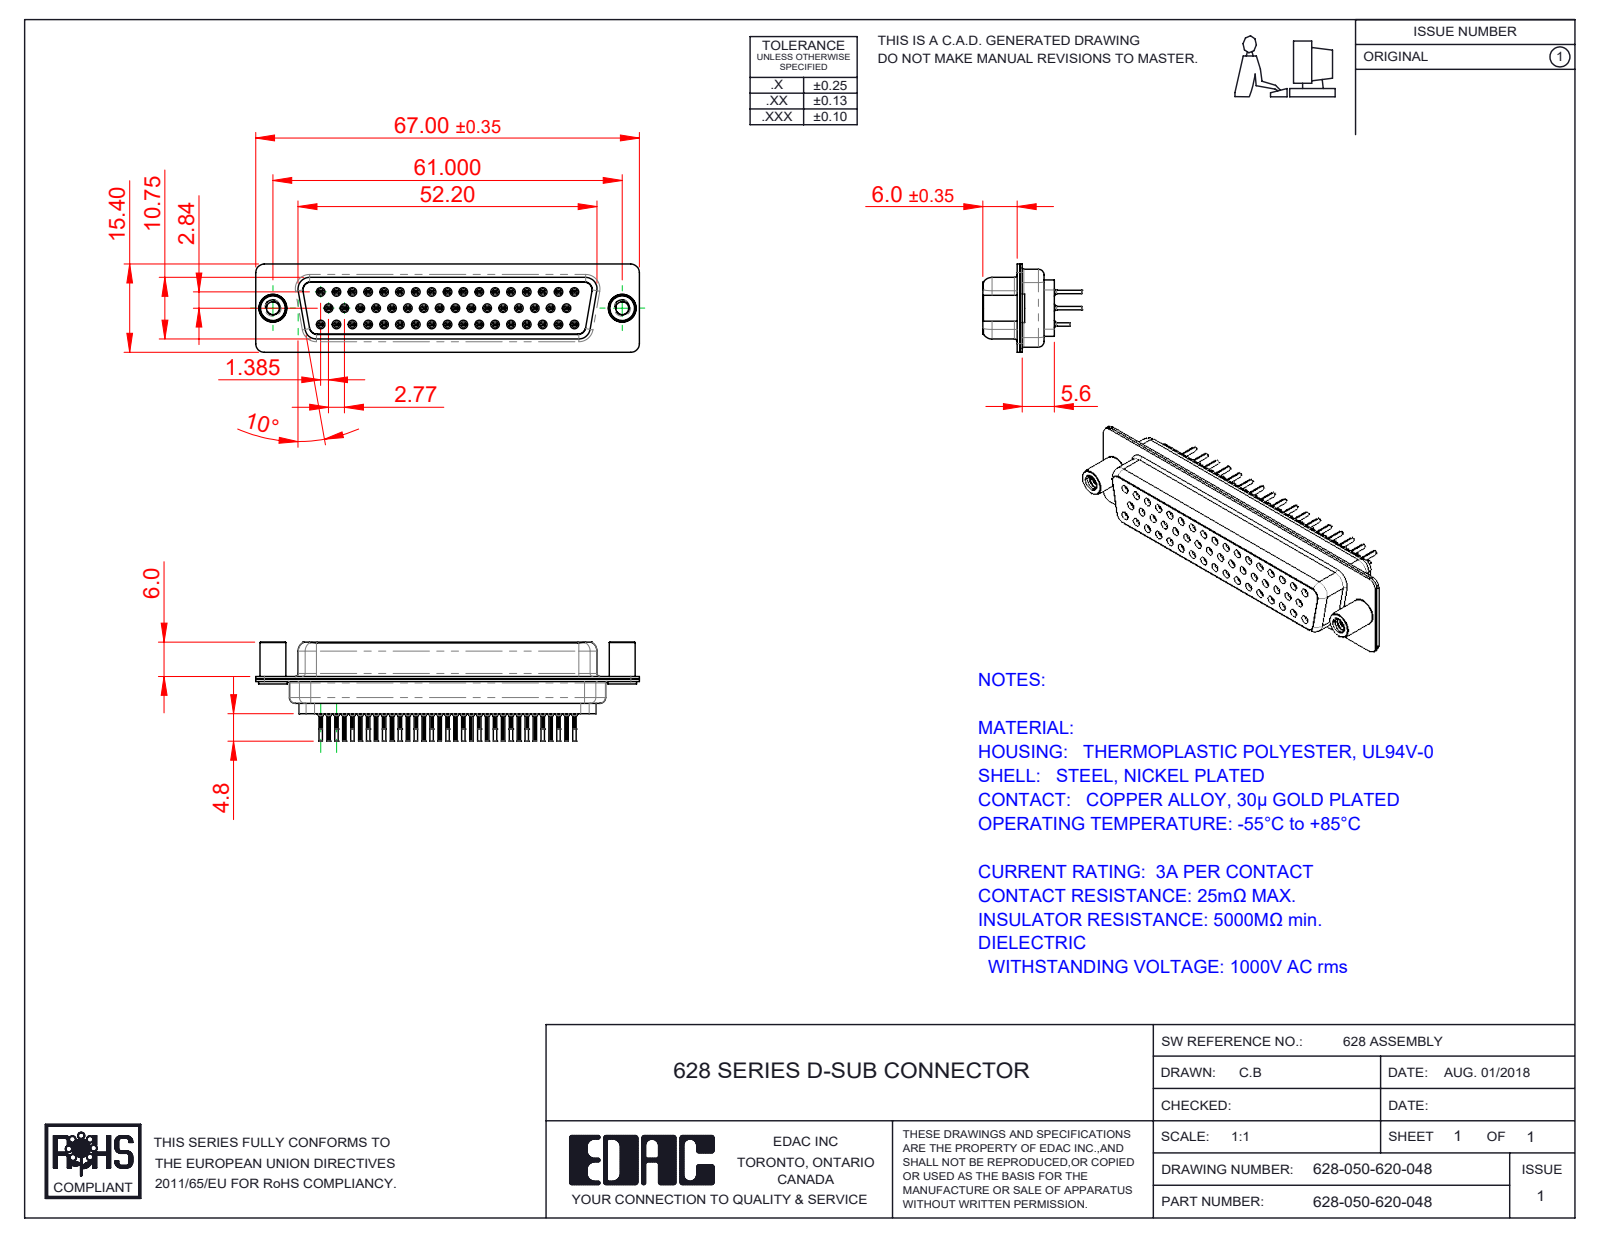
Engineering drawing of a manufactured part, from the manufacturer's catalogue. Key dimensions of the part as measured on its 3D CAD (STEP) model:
Part name (STEP PRODUCT): 628 Contact Row 1_20L; 628 Contact Row 2_20L; 628-050-620-048; 628 Shell Rear_50 Contacts (+4 more)
STEP written by: SolidWorks 2020 (CONFIG_CONTROL_DESIGN)
Units: millimetres
Bodies: 55 solids, 6663 faces (1619 planar, 1815 cylindrical, 3229 other)
Overall size (bounding box): 67 × 17.3 × 15.4
Volume: 6 786 mm³ · Surface area: 15 476 mm²
Round holes (diameter × count): ⌀0.2 ×50, ⌀0.8 ×50, ⌀0.9 ×50, ⌀1.1 ×50, ⌀1.6 ×50, ⌀1.7 ×17, ⌀2.26 ×2, ⌀4 ×2, ⌀4.05 ×2, ⌀4.85 ×2
Round bosses / shafts (diameter × count): ⌀2 ×50, ⌀1.5 ×50, ⌀1.2 ×50, ⌀0.6 ×50, ⌀5 ×2, ⌀4.95 ×2, ⌀4.8 ×2, ⌀4.5 ×2
Partial cylindrical surfaces — rounded edges, fillets, slot ends (radius × count): R0.1 ×100, R0.28 ×33, R1.5 ×16, R2 ×12, R1.35 ×8, R0.25 ×4, R0.5 ×4, R0.6 ×4
Main face-to-face distances: 0.45, 0.4, 11.33, 1.87, 0.9, 10.3, 6.05, 1.8, 6.5, 6.45
Hole centre spacings: 3.16, 2.77, 5.54, 8.31, 11.08, 13.85, 16.62, 19.39
